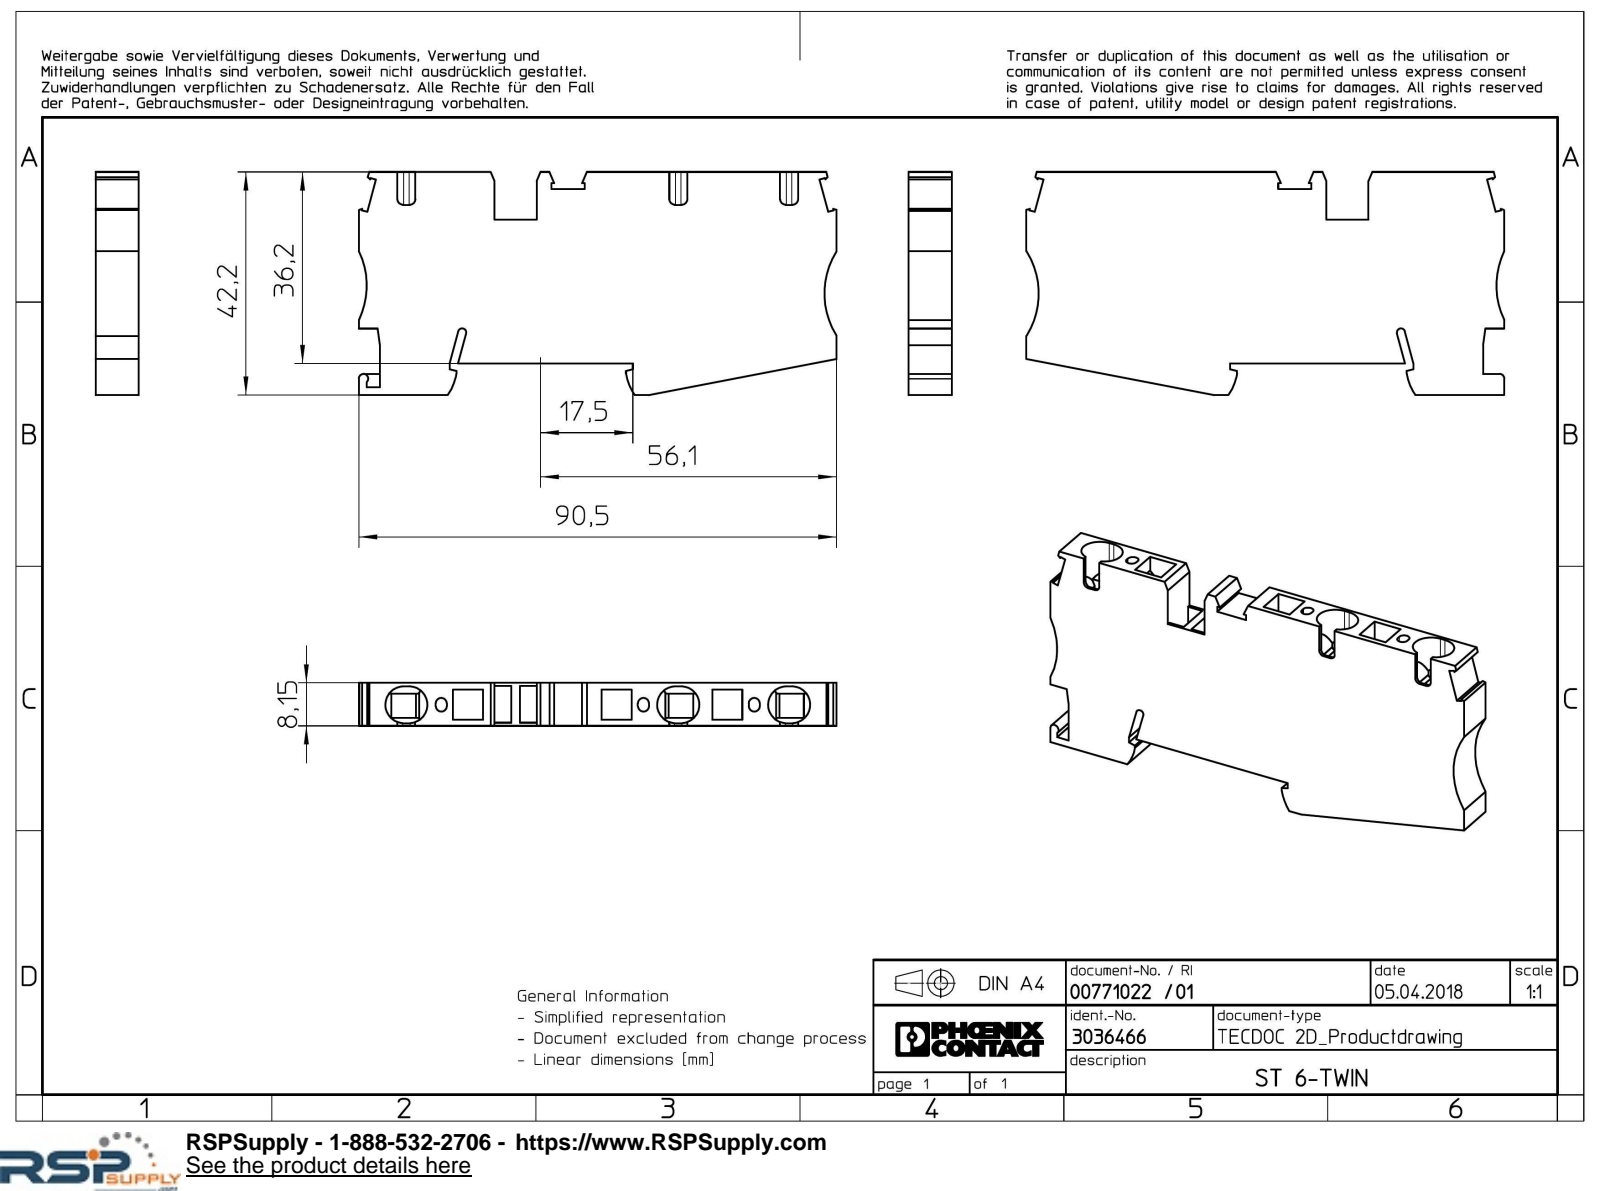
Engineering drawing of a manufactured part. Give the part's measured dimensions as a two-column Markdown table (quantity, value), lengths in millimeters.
| quantity | value |
| --- | --- |
| part name | ST_6_TWIN-select |
| STEP written by | Creo Elements/Direct Modeling 20.1A 29-Sep-2018 (C) Parametric Technology GmbH (AUTOMOTIVE_DESIGN) |
| units | millimeters |
| bodies | 1 solid, 162 faces (137 planar, 25 cylindrical, 0 other) |
| overall size | 90.5 × 42.2 × 8.15 |
| volume | 23 528 mm³ |
| surface area | 11 605 mm² |
| partial cylindrical surfaces (radius × count) | 1 × 6, 1.05 × 6, 3.5 × 6, 9.5 × 2, 15 × 2, 0.7 × 1, 0.8 × 1, 0.9 × 1 |
| main face-to-face distances | 8.15, 4.6, 36.2, 7, 3.15, 4.85, 0.57, 1.5, 6, 8 |
